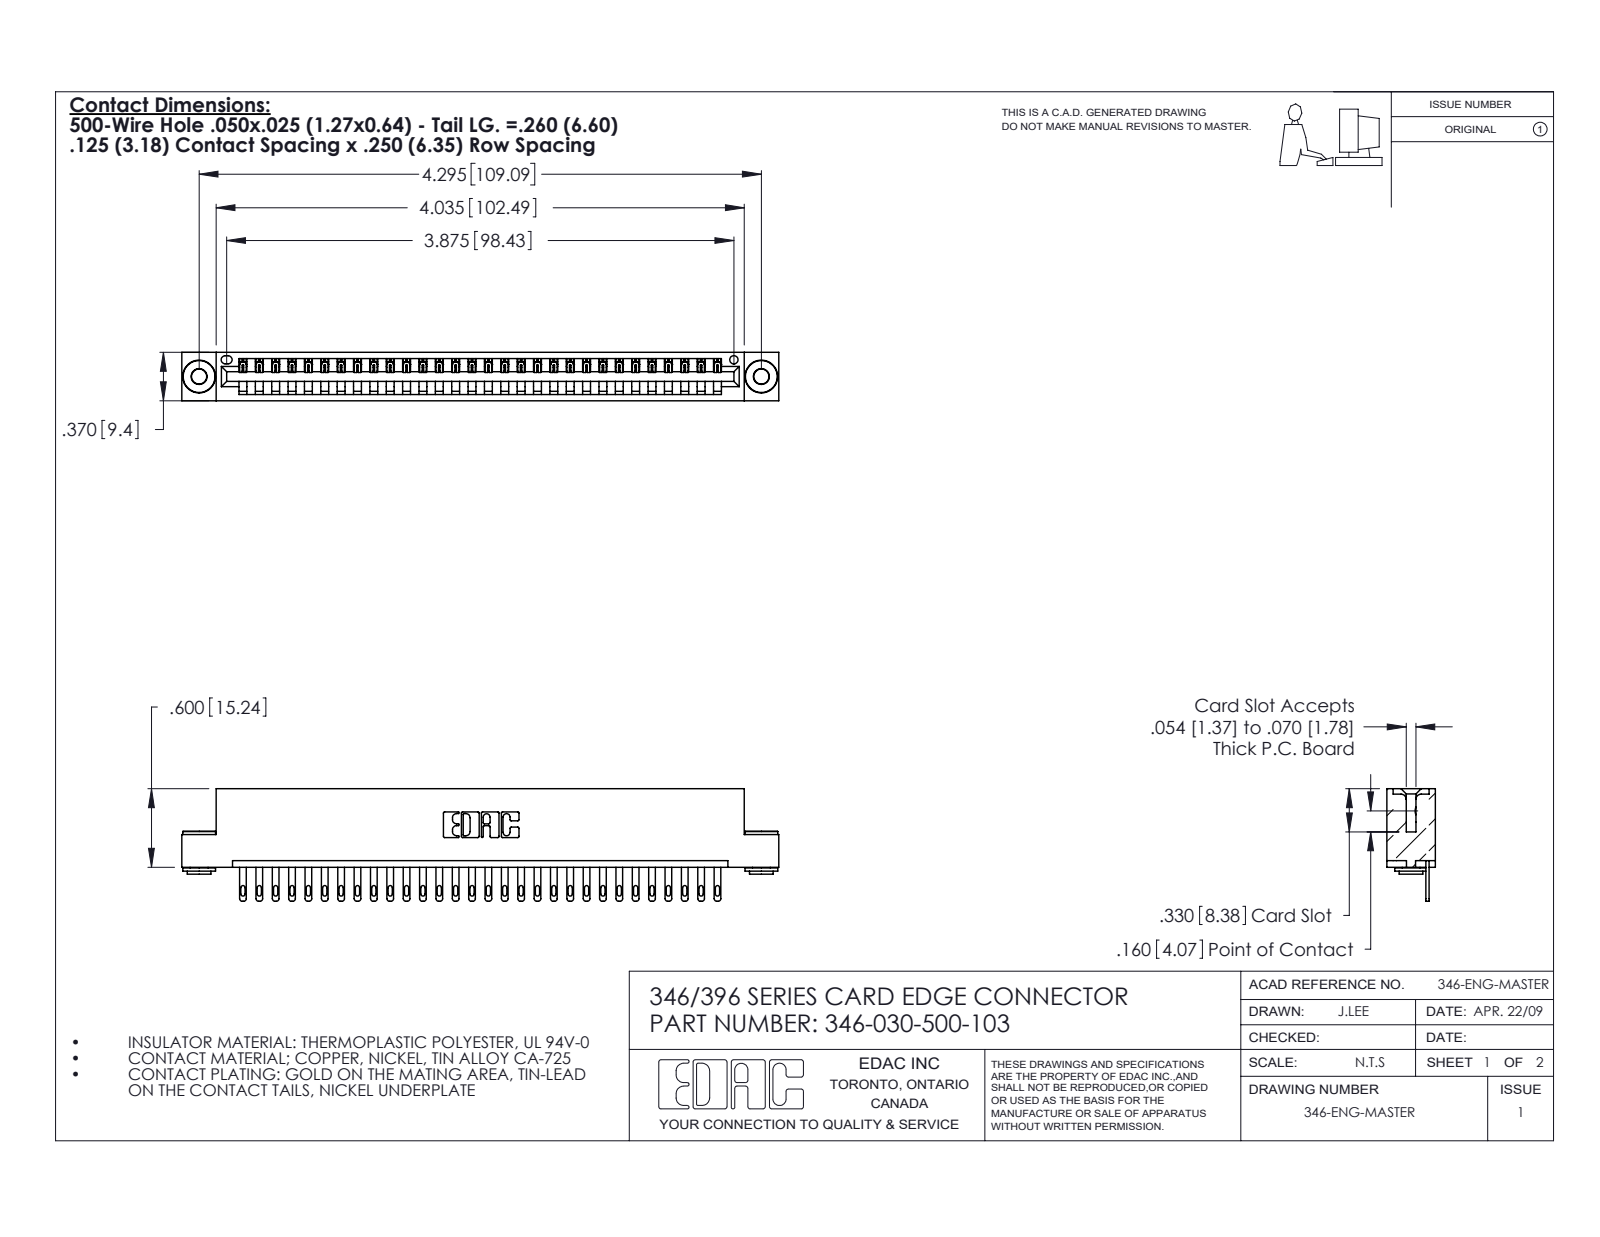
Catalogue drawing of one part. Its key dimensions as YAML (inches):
part_name: "345-250-002_345-250-002-102; 346 Part_Flush Mounting Lugs - 0.156 Dia-TH; 345-292-001_345-293-100; 346-030-500-103"
step_written_by: "SolidWorks 2020 (CONFIG_CONTROL_DESIGN)"
units: inches
bodies: {solids: 33, faces: 1794, planar: 1120, cylindrical: 666, other: 8}
overall_size: [4.56, 0.86, 0.37]
volume: 0.673
surface_area: 21.65
round_holes:
  - {diameter: 0.116, count: 2}
  - {diameter: 0.156, count: 2}
  - {diameter: 0.064, count: 1}
round_bosses_or_shafts:
  - {diameter: 0.25, count: 2}
  - {diameter: 0.18, count: 2}
  - {diameter: 0.136, count: 2}
partial_cylinders:
  - {radius: 0.006, count: 60}
  - {radius: 0.016, count: 60}
  - {radius: 0.02, count: 60}
  - {radius: 0.01, count: 22}
  - {radius: 0.007, count: 6}
  - {radius: 0.031, count: 6}
  - {radius: 0.026, count: 3}
  - {radius: 0.031, count: 2}
face_to_face_distances: [0.048, 0.322, 0.25, 0.37, 0.025, 0.072, 0.298, 0.148, 0.222, 0.1]
hole_center_spacings: [0.246, 4.087, 4.295]
